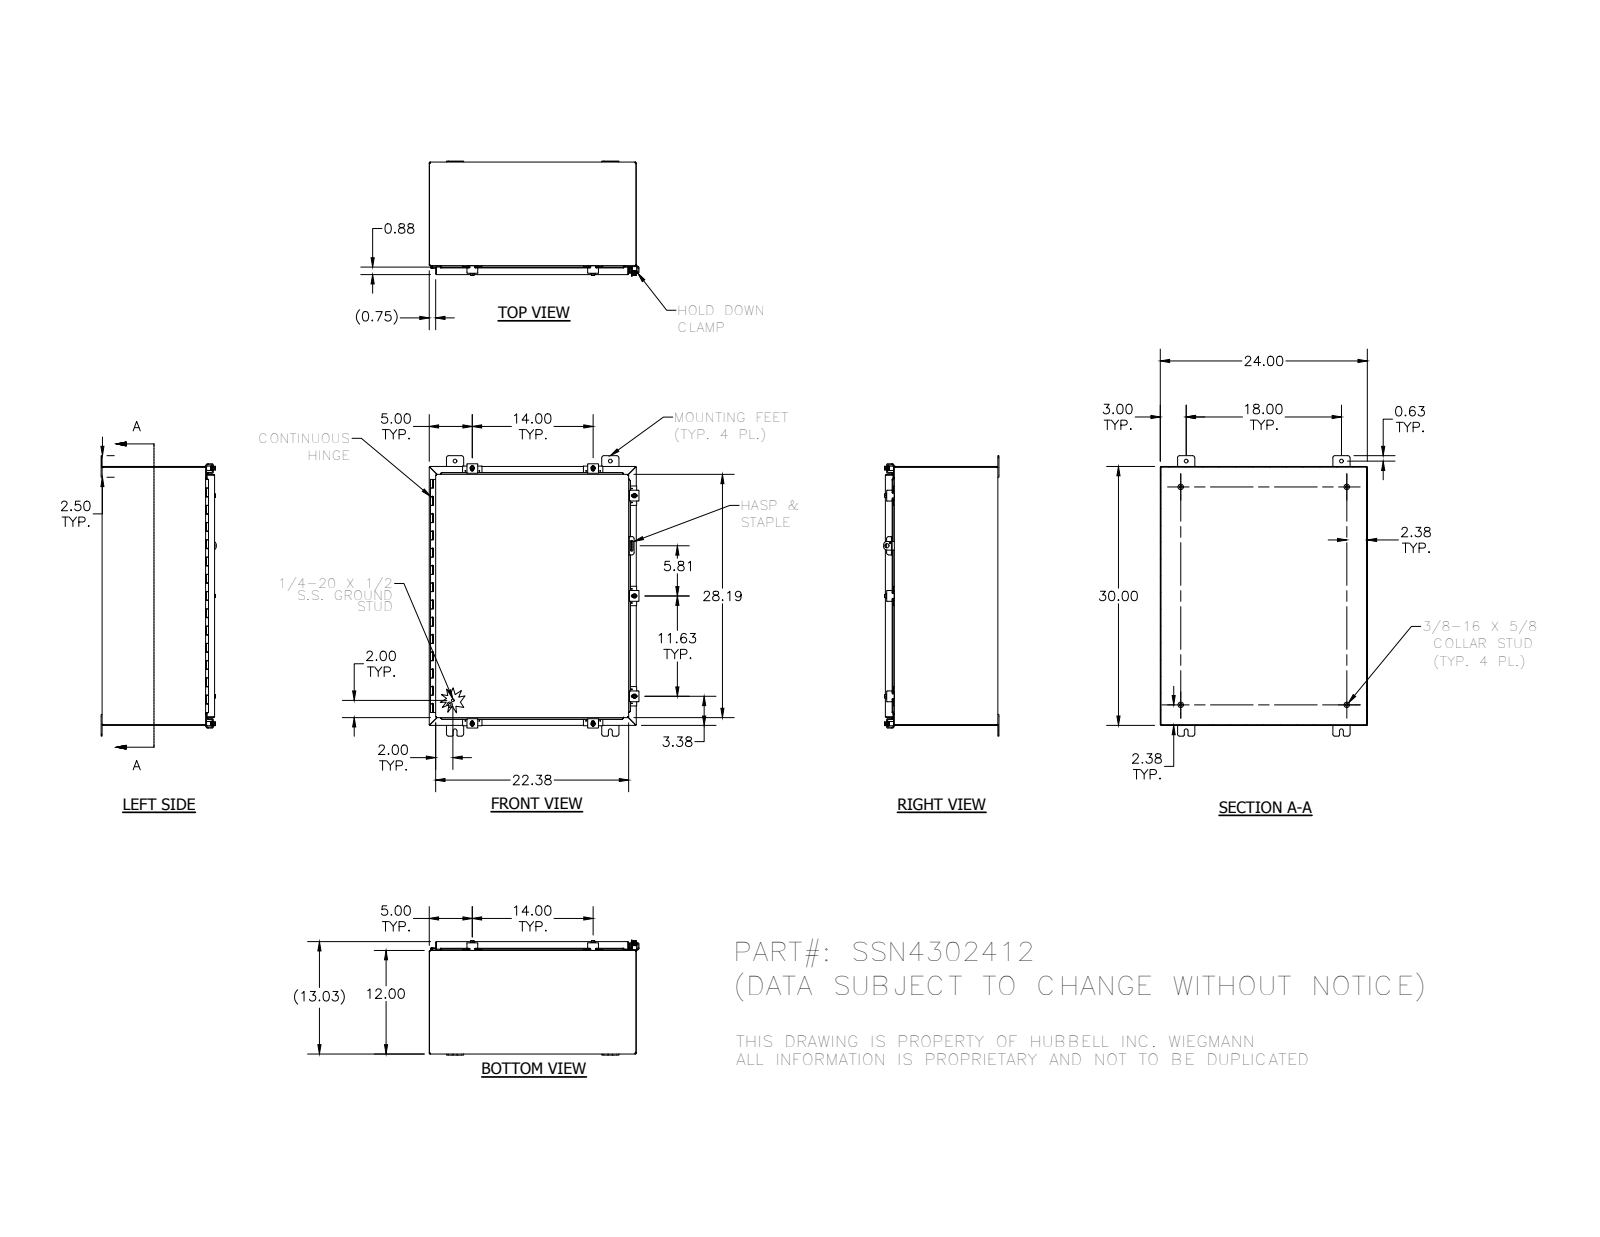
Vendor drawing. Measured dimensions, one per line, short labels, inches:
name: 38412; SSN43024LID; SSN4302412; 38846 (+8 more)
written by: SolidWorks 2014 (AUTOMOTIVE_DESIGN)
unit: in
bodies: 52 solids, 2111 faces (805 planar, 935 cylindrical, 371 other)
size: 32.5 × 24.311 × 13.355
volume: 239.9 in³; area: 6 334 in²
holes: 14× ⌀0.11, 7× ⌀0.211, 7× ⌀0.281, 7× ⌀0.3, 4× ⌀0.438, 1× ⌀0.125, 1× ⌀0.156, 1× ⌀0.5
bosses: 9× ⌀0.25, 7× ⌀0.52, 7× ⌀0.5, 7× ⌀0.35, 4× ⌀0.625, 4× ⌀0.33, 2× ⌀0.115, 1× ⌀0.337
rounds: 83× R0.03, 37× R0.125, 33× R0.25, 23× R0.031, 23× R0.105, 15× R0.062, 14× R0.141, 10× R0.1
face distances: 0.074, 12.959, 23.926, 12.885, 13.033, 29.926, 23.852, 24, 29.852, 30
hole spacings: 0.876, 29.3, 14, 1.625, 13.191, 14.816, 28.961, 29.006
